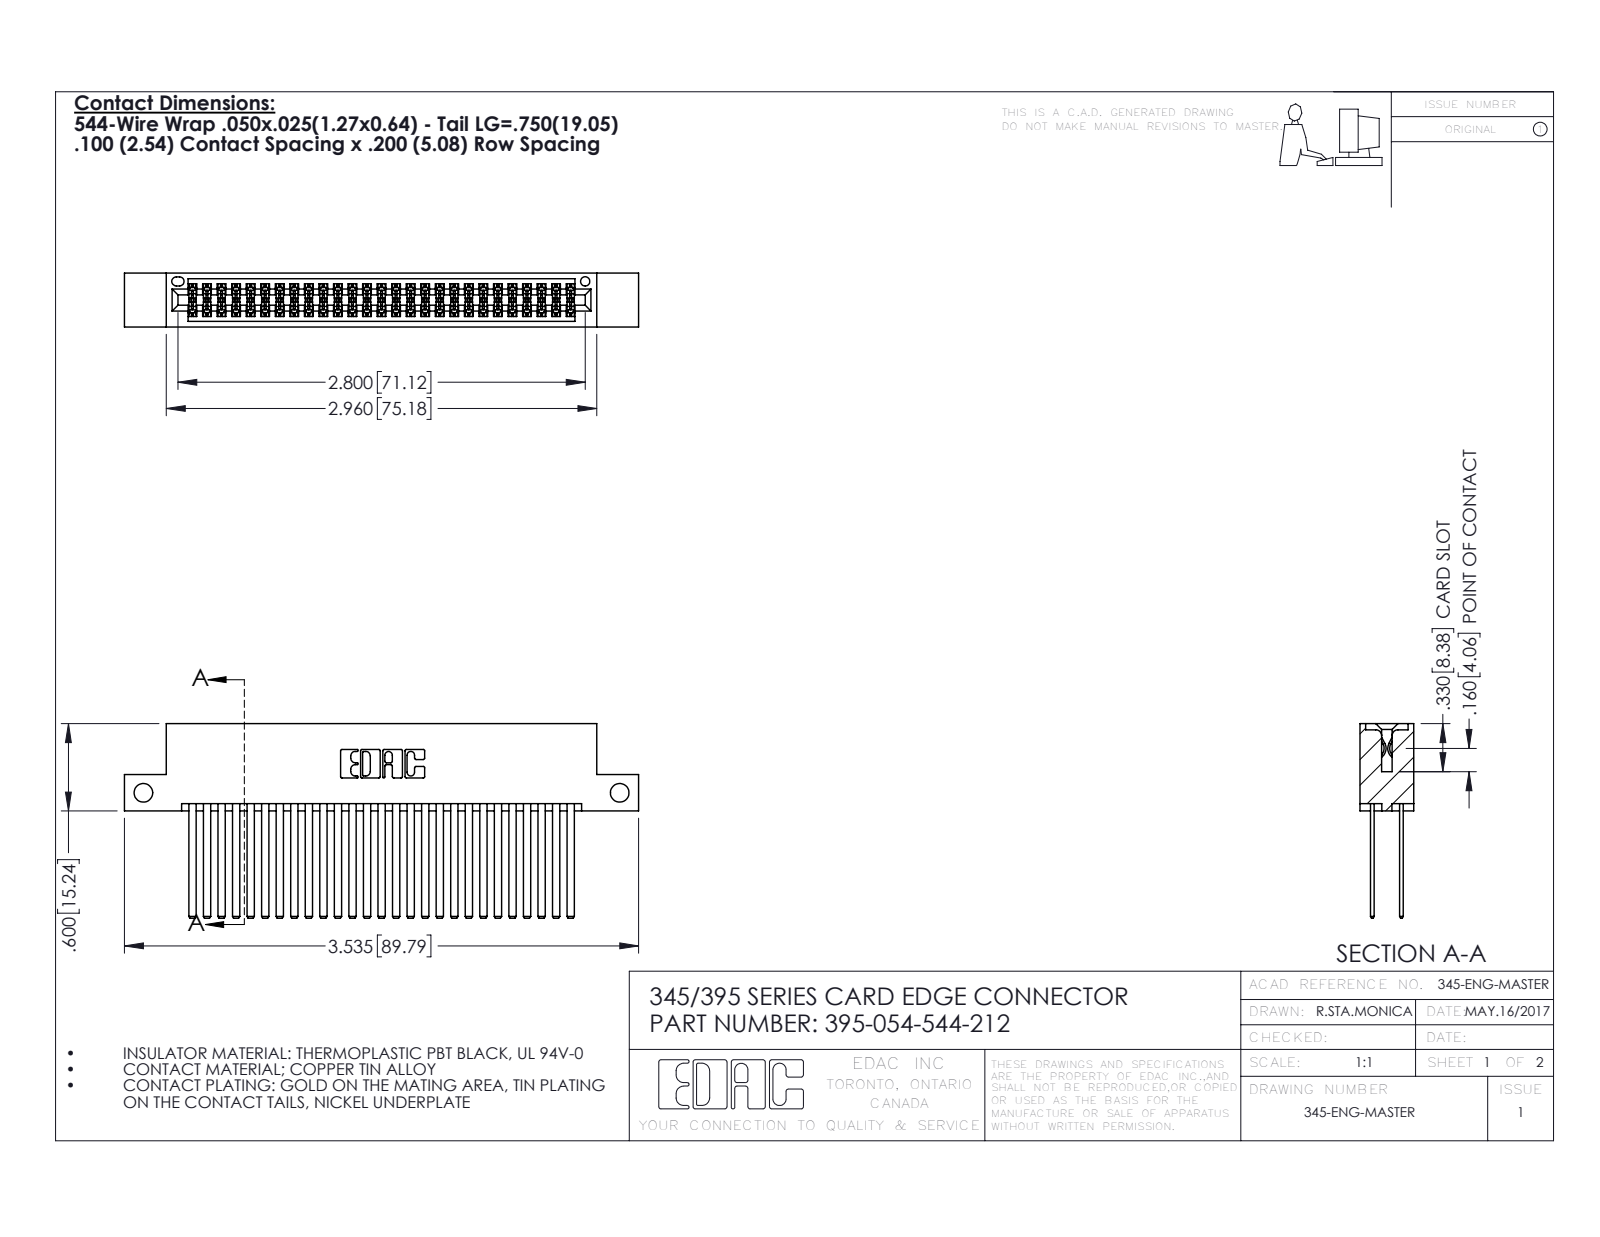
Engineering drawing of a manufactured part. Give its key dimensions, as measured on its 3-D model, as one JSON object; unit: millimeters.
{"part_name": "345 Part_Flush Mounting Lugs - Side Mount; 345-292-001_345-293-144; 395-054-544-212", "step_written_by": "SolidWorks 2016 (CONFIG_CONTROL_DESIGN)", "units": "millimeters", "bodies": {"solids": 55, "faces": 2502, "planar": 1646, "cylindrical": 856, "other": 0}, "overall_size": [89.8, 34, 9.4], "volume_mm3": 9260, "surface_area_mm2": 15470, "round_holes": [[3.3, 2], [1.6, 1]], "partial_cylinders_radius": [[0.2, 81], [0.3, 22], [0.2, 6], [0.8, 6], [0.7, 3], [0.4, 2], [0.5, 2], [0.6, 2]], "face_to_face_distances": [5.1, 0.6, 7.6, 1.8, 2.5, 6.9, 5.7, 4.4, 9.4, 1.3], "hole_center_spacings": [83.2]}
